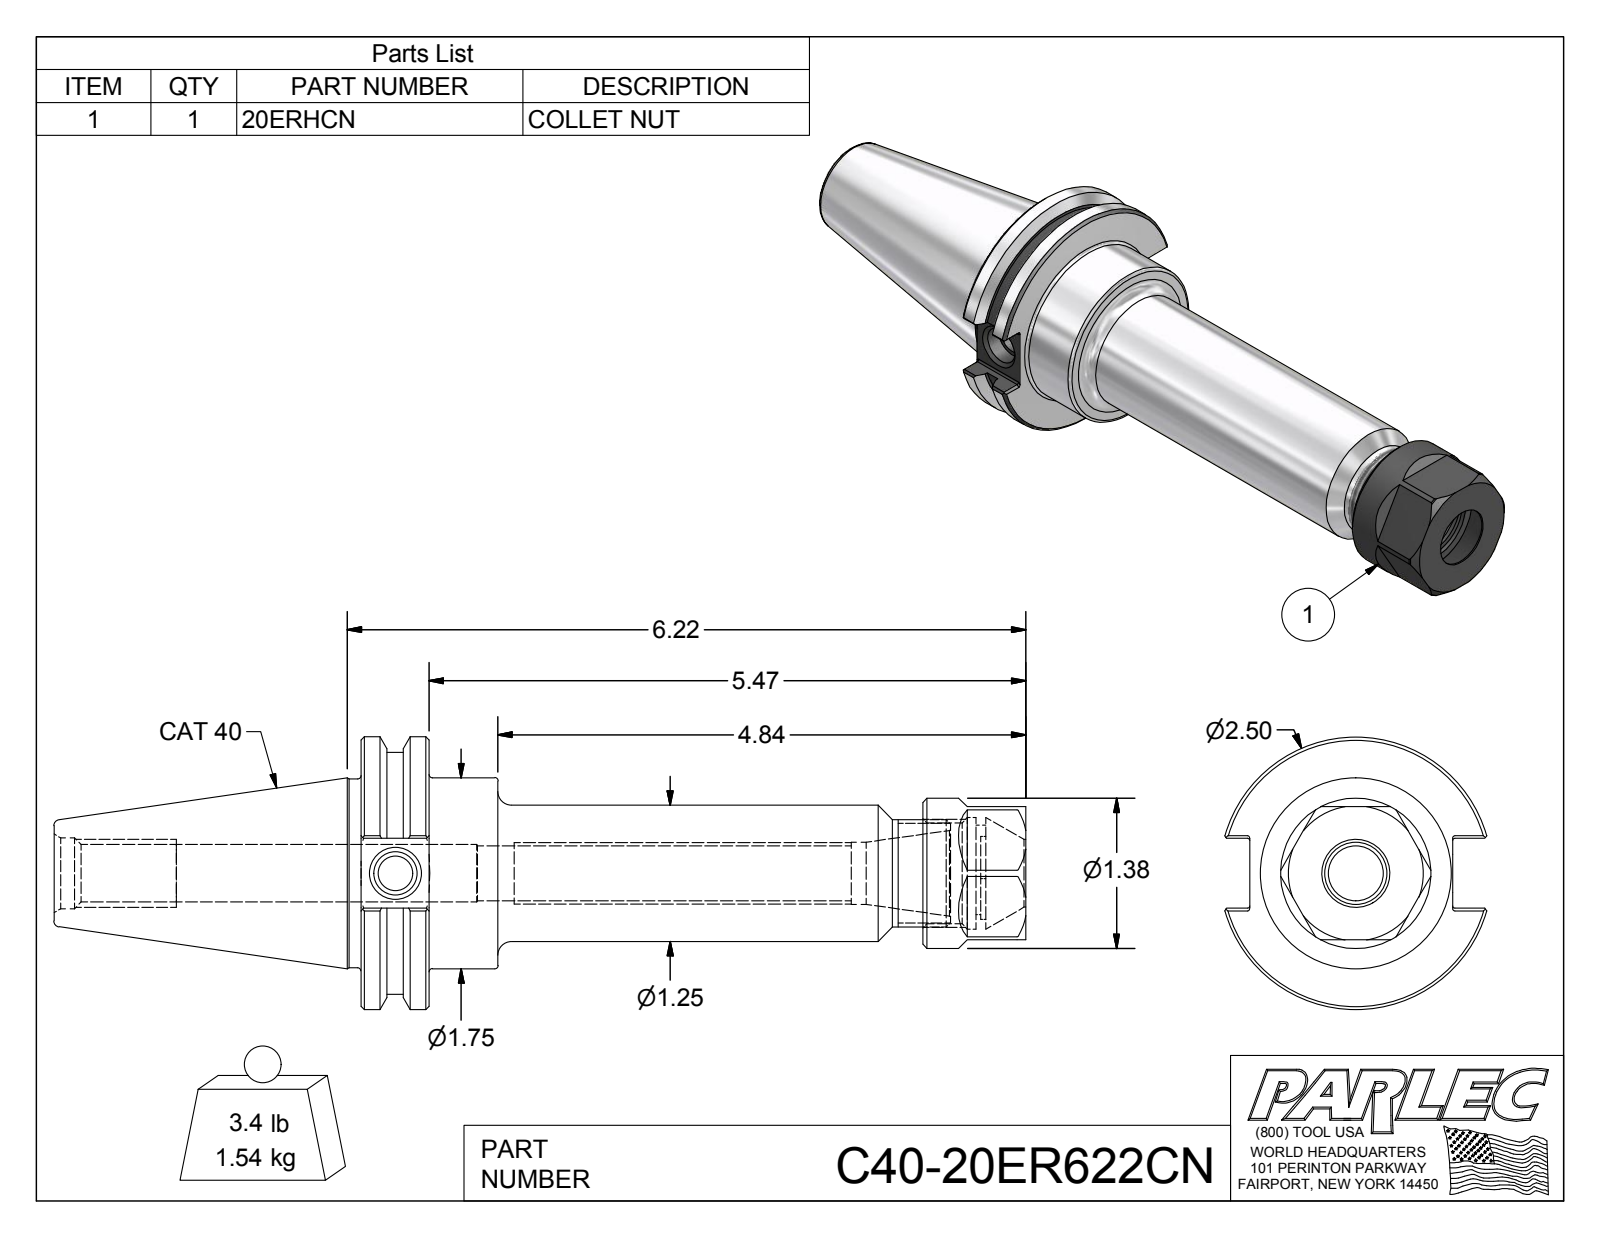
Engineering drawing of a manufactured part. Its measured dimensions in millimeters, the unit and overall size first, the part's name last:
Units: millimetres
Overall size (bounding box): 226.3 × 63.5 × 61
Round holes (diameter × count): ⌀8 ×1, ⌀10.1 ×1, ⌀12.8 ×1, ⌀13.4 ×1, ⌀13.4 ×1, ⌀14.5 ×1, ⌀15.7 ×1, ⌀16.5 ×1, ⌀20.8 ×1, ⌀23.5 ×1, ⌀26 ×1
Round bosses / shafts (diameter × count): ⌀63.5 ×1, ⌀56.4 ×1, ⌀44.5 ×1, ⌀43.9 ×1, ⌀35 ×1, ⌀31.8 ×1, ⌀25 ×1
Partial cylindrical surfaces — rounded edges, fillets, slot ends (radius × count): R0.5 ×12, R10.7 ×1
Main face-to-face distances: 15.9, 154.8, 138.9, 31, 130.8, 114.9, 24, 31.9, 16, 98.9
Hole centre spacings: 0.9
Volume: 197 800 mm³ · Surface area: 43 080 mm²
Bodies: 2 solids, 126 faces (50 planar, 35 cylindrical, 41 other)
Part name (STEP PRODUCT): C40-20ER622CN; 20ERHCN; C40-20ER6-1
STEP written by: Autodesk Inventor 2012 (AUTOMOTIVE_DESIGN)
